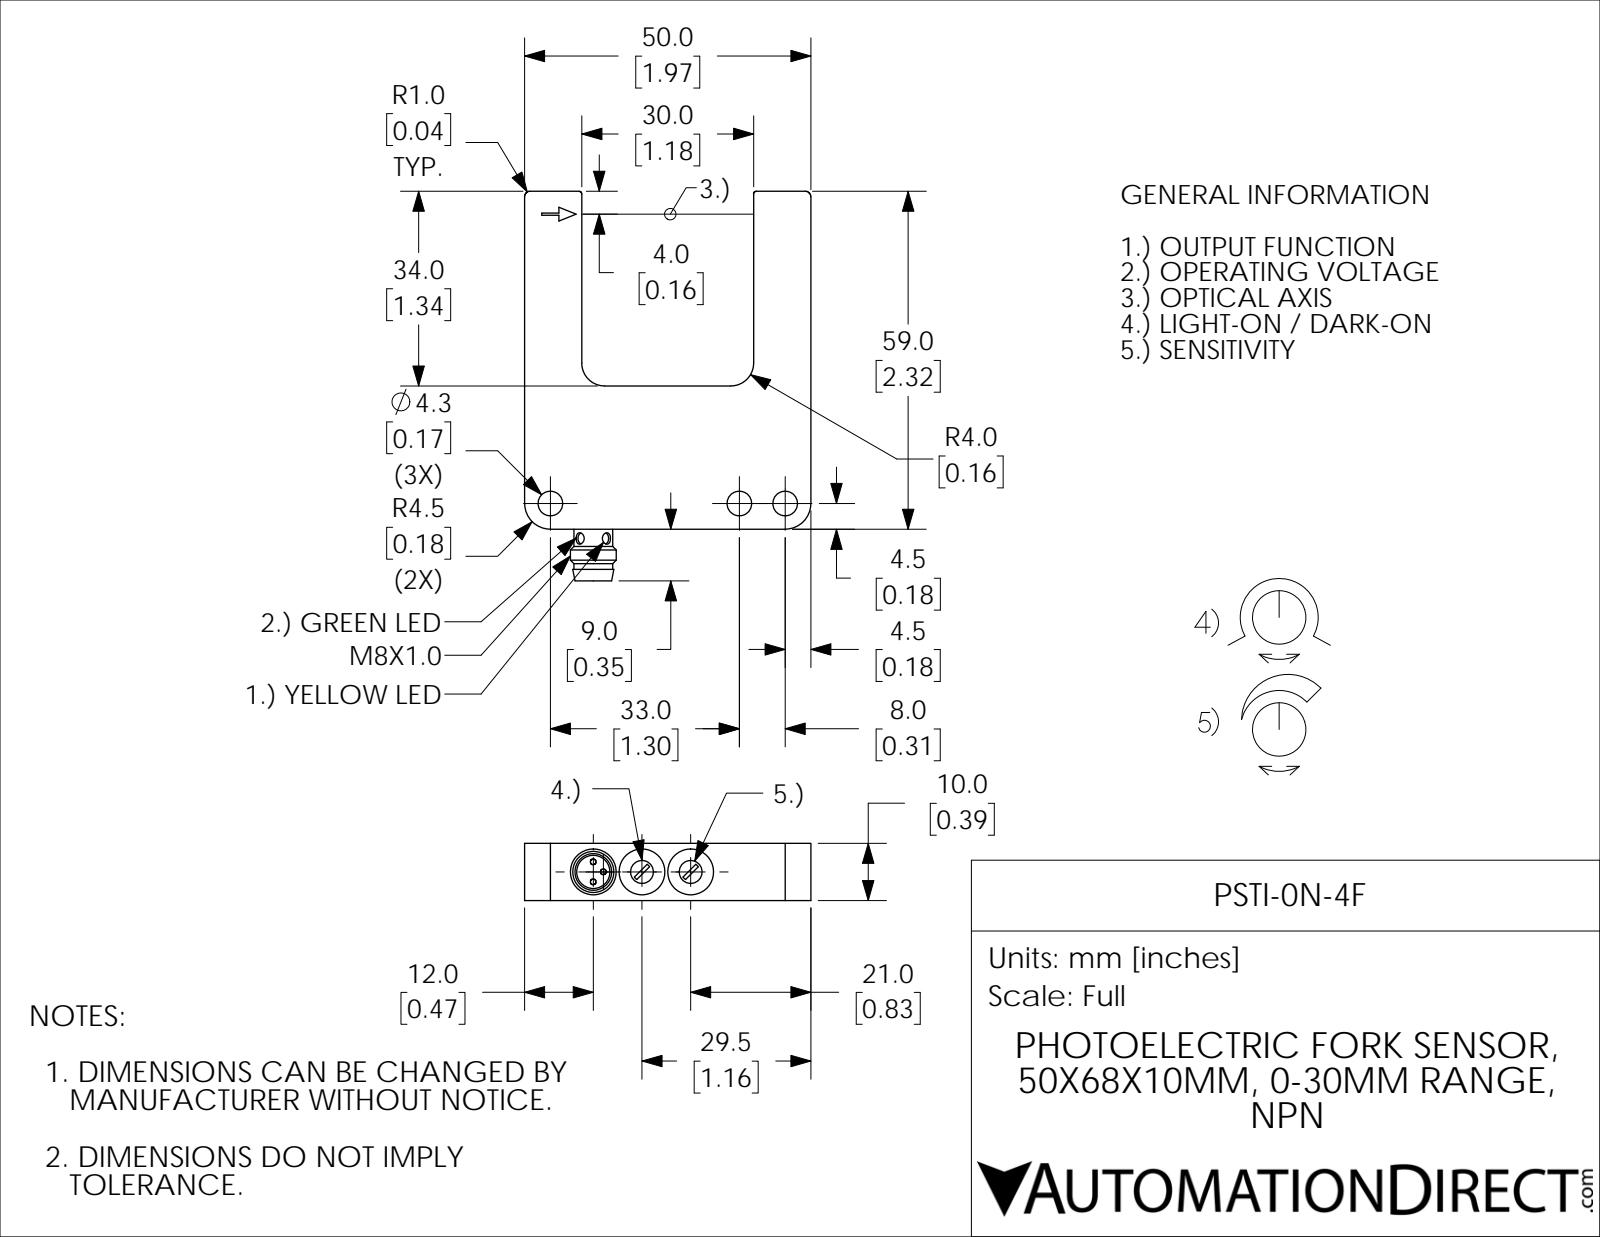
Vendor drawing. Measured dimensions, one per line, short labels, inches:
name: PSTI-0N-4F
written by: SolidWorks 2017 (AUTOMOTIVE_DESIGN)
unit: in
bodies: 1 solid, 71 faces (35 planar, 30 cylindrical, 6 other)
size: 2.677 × 1.969 × 0.394
volume: 1.163 in³; area: 11.35 in²
holes: 3× ⌀0.169, 2× ⌀0.079, 2× ⌀0.157, 2× ⌀0.315, 1× ⌀0.228
bosses: 3× ⌀0.039, 1× ⌀0.315, 1× ⌀0.267
rounds: 2× R0.02, 2× R0.039, 2× R0.063, 2× R0.157, 2× R0.177
face distances: 0.394, 1.575, 1.969, 1.181, 0.984, 1.339, 2.323, 2.319, 0.98, 0.157
hole spacings: 0.335, 0.315, 0.669, 1.299, 1.614
